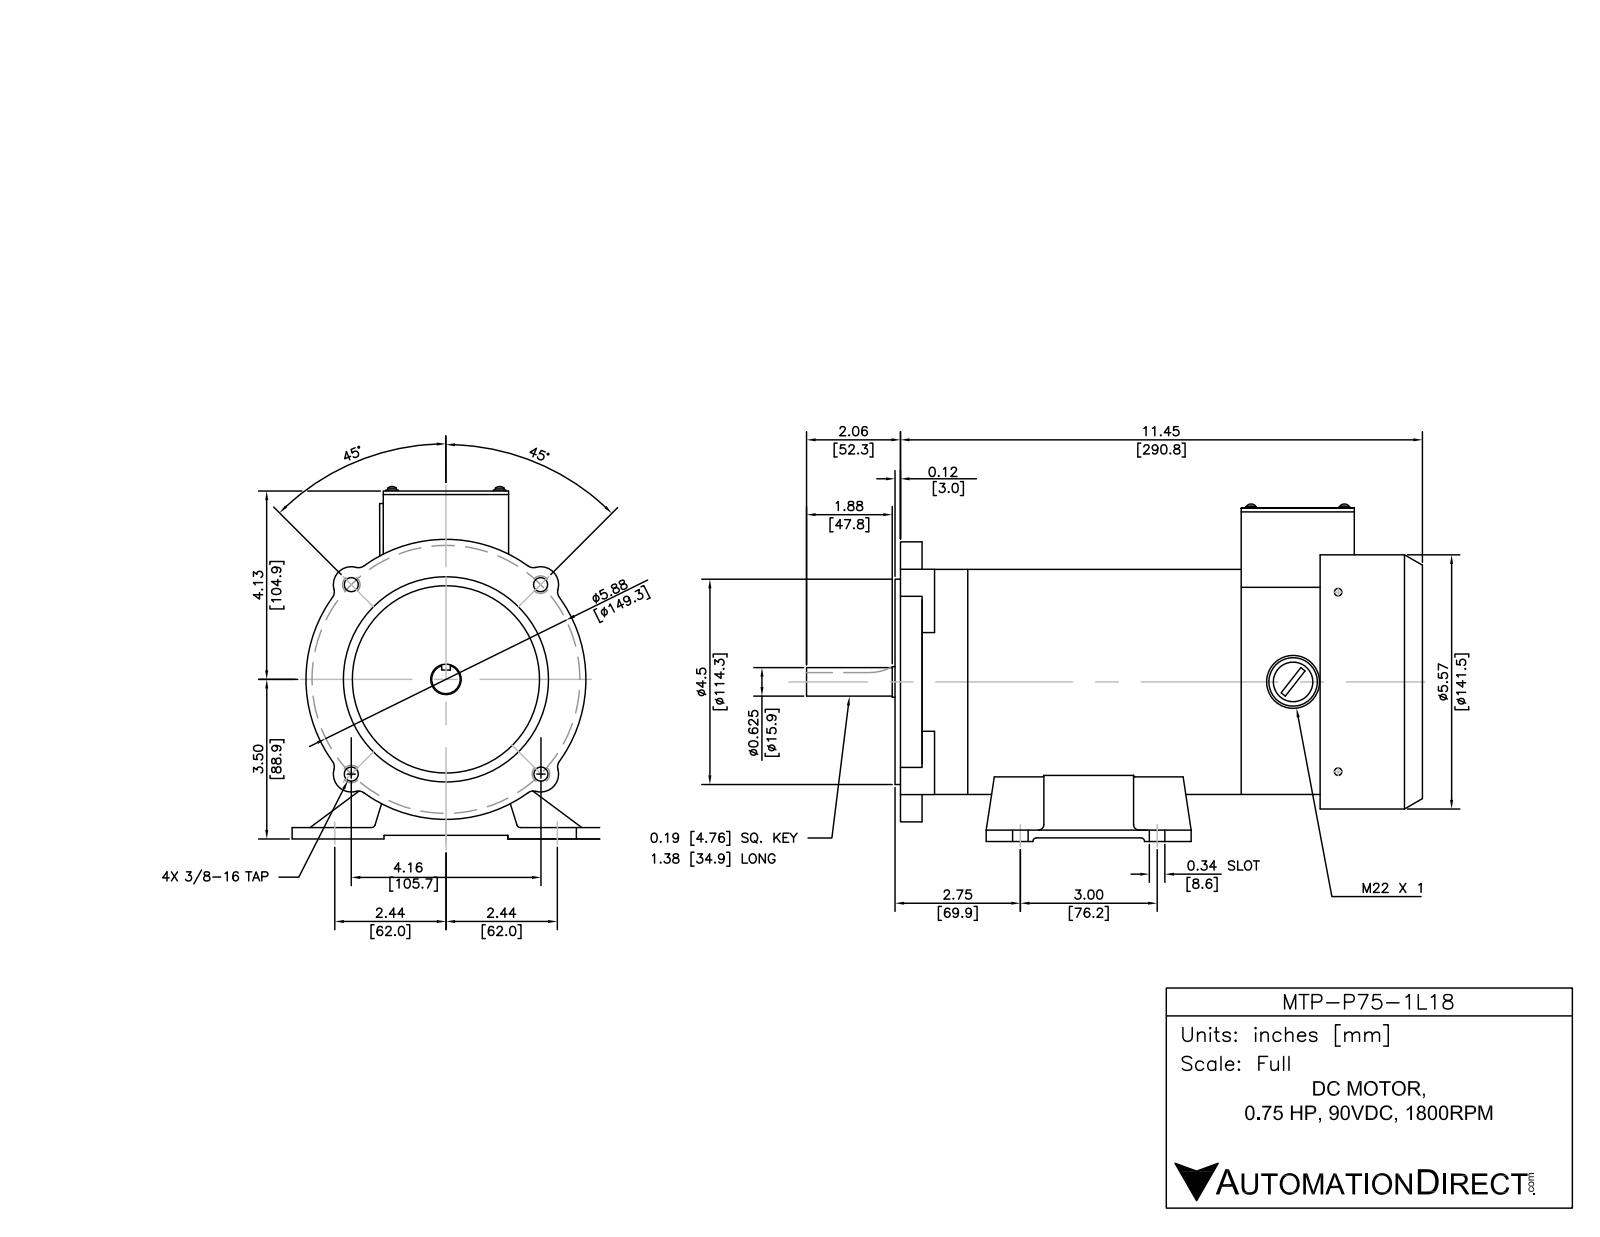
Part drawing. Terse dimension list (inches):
name: WPMDC34-18-90-180-56CB b
written by: SolidWorks 2017 (AUTOMOTIVE_DESIGN)
unit: in
bodies: 33 solids, 1822 faces (567 planar, 859 cylindrical, 396 other)
size: 14.339 × 7.521 × 6.496
volume: 73.75 in³; area: 829.4 in²
holes: 10× ⌀0.13, 8× ⌀0.197, 2× ⌀0.067, 2× ⌀0.169, 2× ⌀0.205, 2× ⌀0.236, 2× ⌀0.276, 2× ⌀0.299, 2× ⌀0.374, 2× ⌀0.394, 2× ⌀0.701, 2× ⌀0.728
bosses: 10× ⌀0.157, 8× ⌀0.354, 8× ⌀0.331, 2× ⌀1.063, 2× ⌀0.39, 1× ⌀6.142, 1× ⌀5.575, 1× ⌀5.512
rounds: 70× R0.02, 38× R0.197, 28× R0.039, 18× R0.098, 10× R0.236, 9× R0.394, 8× R0.118, 8× R0.157
face distances: 0.098, 0.079, 0.157, 0.059, 10.803, 1.535, 10.744, 0.031, 10.646, 1.504
hole spacings: 1.187, 2.166, 2.262, 2.362, 2.749, 0.103, 1.42, 1.726
